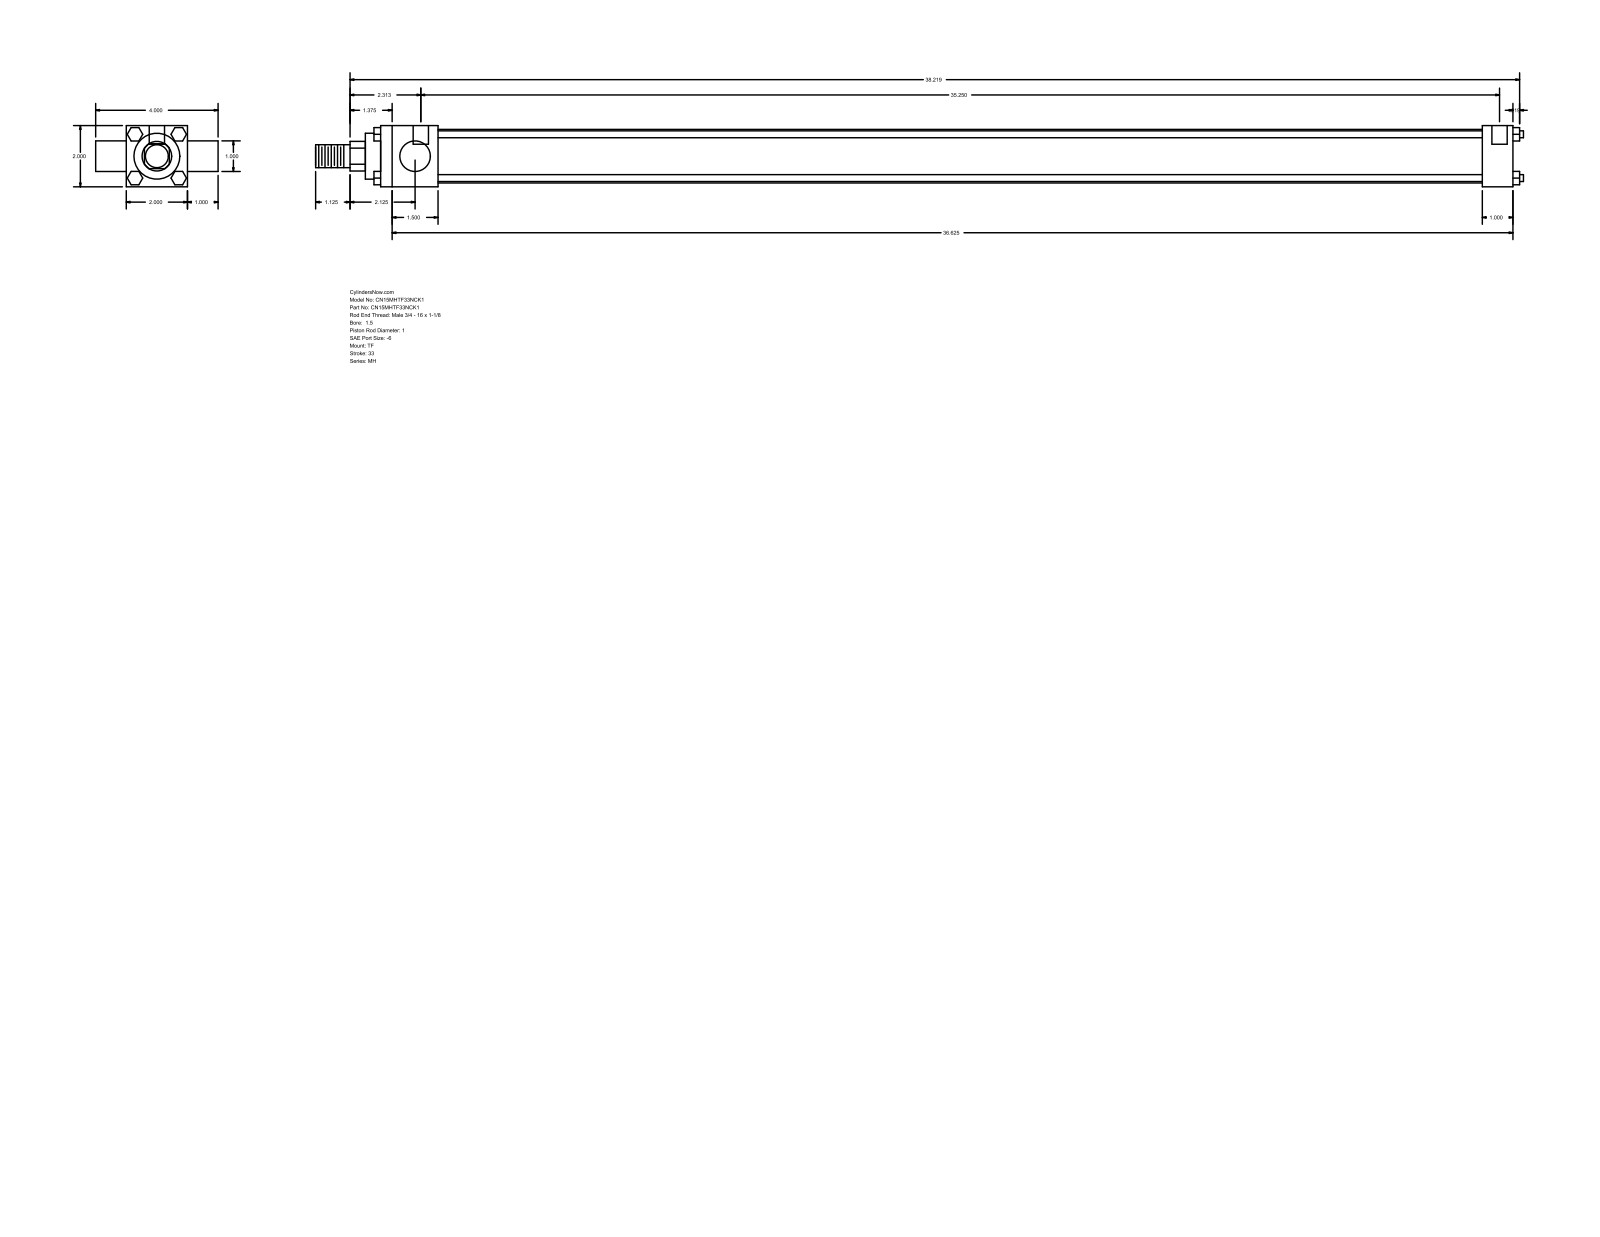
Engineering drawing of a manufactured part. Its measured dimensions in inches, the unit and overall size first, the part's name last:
Units: inches
Overall size (bounding box): 39.469 × 4 × 2
Round holes (diameter × count): ⌀0.219 ×3, ⌀0.5 ×2
Round bosses / shafts (diameter × count): ⌀0.225 ×4, ⌀1 ×2, ⌀1.75 ×1, ⌀1.5 ×1, ⌀0.75 ×1
Partial cylindrical surfaces — rounded edges, fillets, slot ends (radius × count): R0.484 ×1
Main face-to-face distances: 2, 1, 37, 3, 1.875, 35.125, 36, 34.125, 4, 0.5
Hole centre spacings: 0.125, 35.25, 35.375
Bodies: 0 solids, 120 faces (92 planar, 28 cylindrical, 0 other)
Part name (STEP PRODUCT): MH_TF__0150_1
STEP written by: GSSL Pune (CONFIG_CONTROL_DESIGN)
